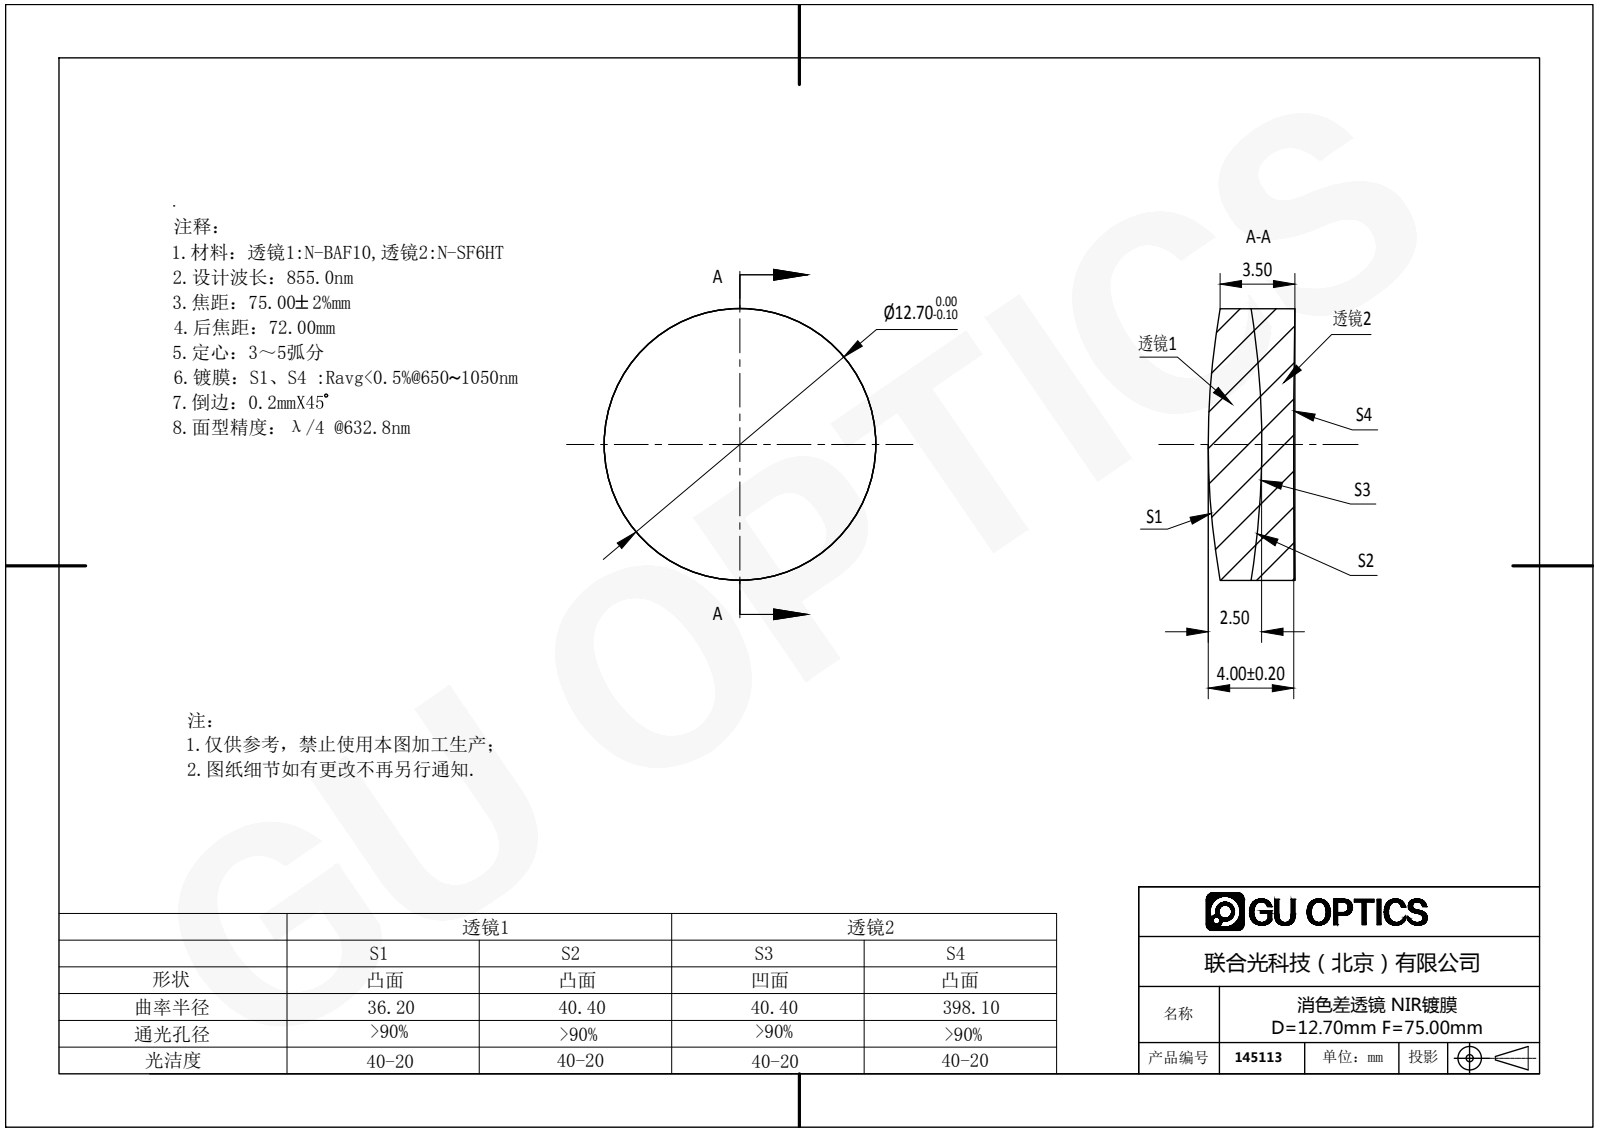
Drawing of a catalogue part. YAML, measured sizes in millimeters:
part_name: "145113"
step_written_by: "SolidWorks 2016 (AUTOMOTIVE_DESIGN)"
units: millimeters
bodies: {solids: 2, faces: 12, planar: 0, cylindrical: 4, other: 8}
overall_size: [12.7, 12.7, 4.05]
volume: 474
surface_area: 649
round_bosses_or_shafts:
  - {diameter: 12.7, count: 1}
